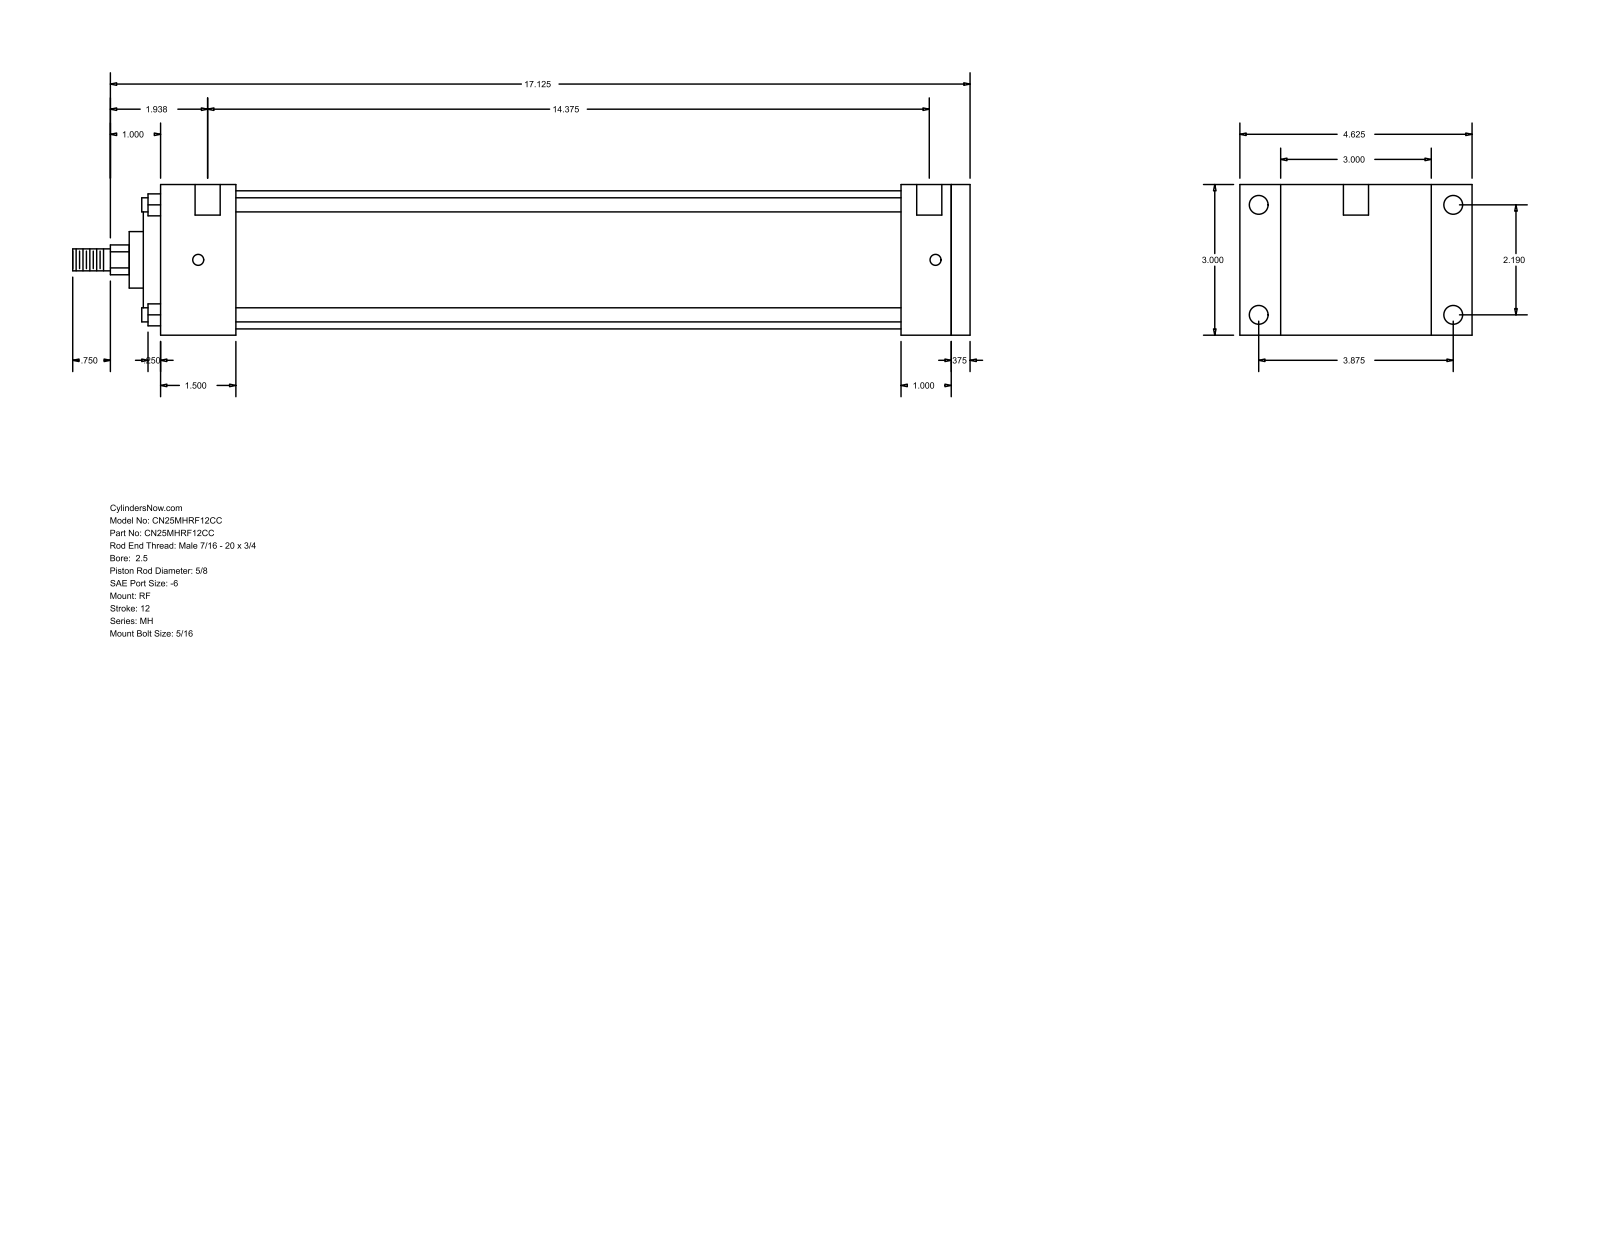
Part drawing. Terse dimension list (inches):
name: MH_RF__0250_0.625
written by: GSSL Pune (CONFIG_CONTROL_DESIGN)
unit: in
bodies: 0 solids, 94 faces (65 planar, 29 cylindrical, 0 other)
size: 17.875 × 4.625 × 3
holes: 4× ⌀0.219, 4× ⌀0.375, 2× ⌀0.5
bosses: 4× ⌀0.281, 1× ⌀2.75, 1× ⌀2.187, 1× ⌀1.125, 1× ⌀0.625, 1× ⌀0.437
rounds: 1× R0.297
face distances: 3, 0.375, 16.125, 15.75, 1, 1.375, 1.5, 14.75, 13.25, 14.25
hole spacings: 2.19, 3.875, 4.451, 14.687, 0.125, 0.187, 14.375, 14.5
